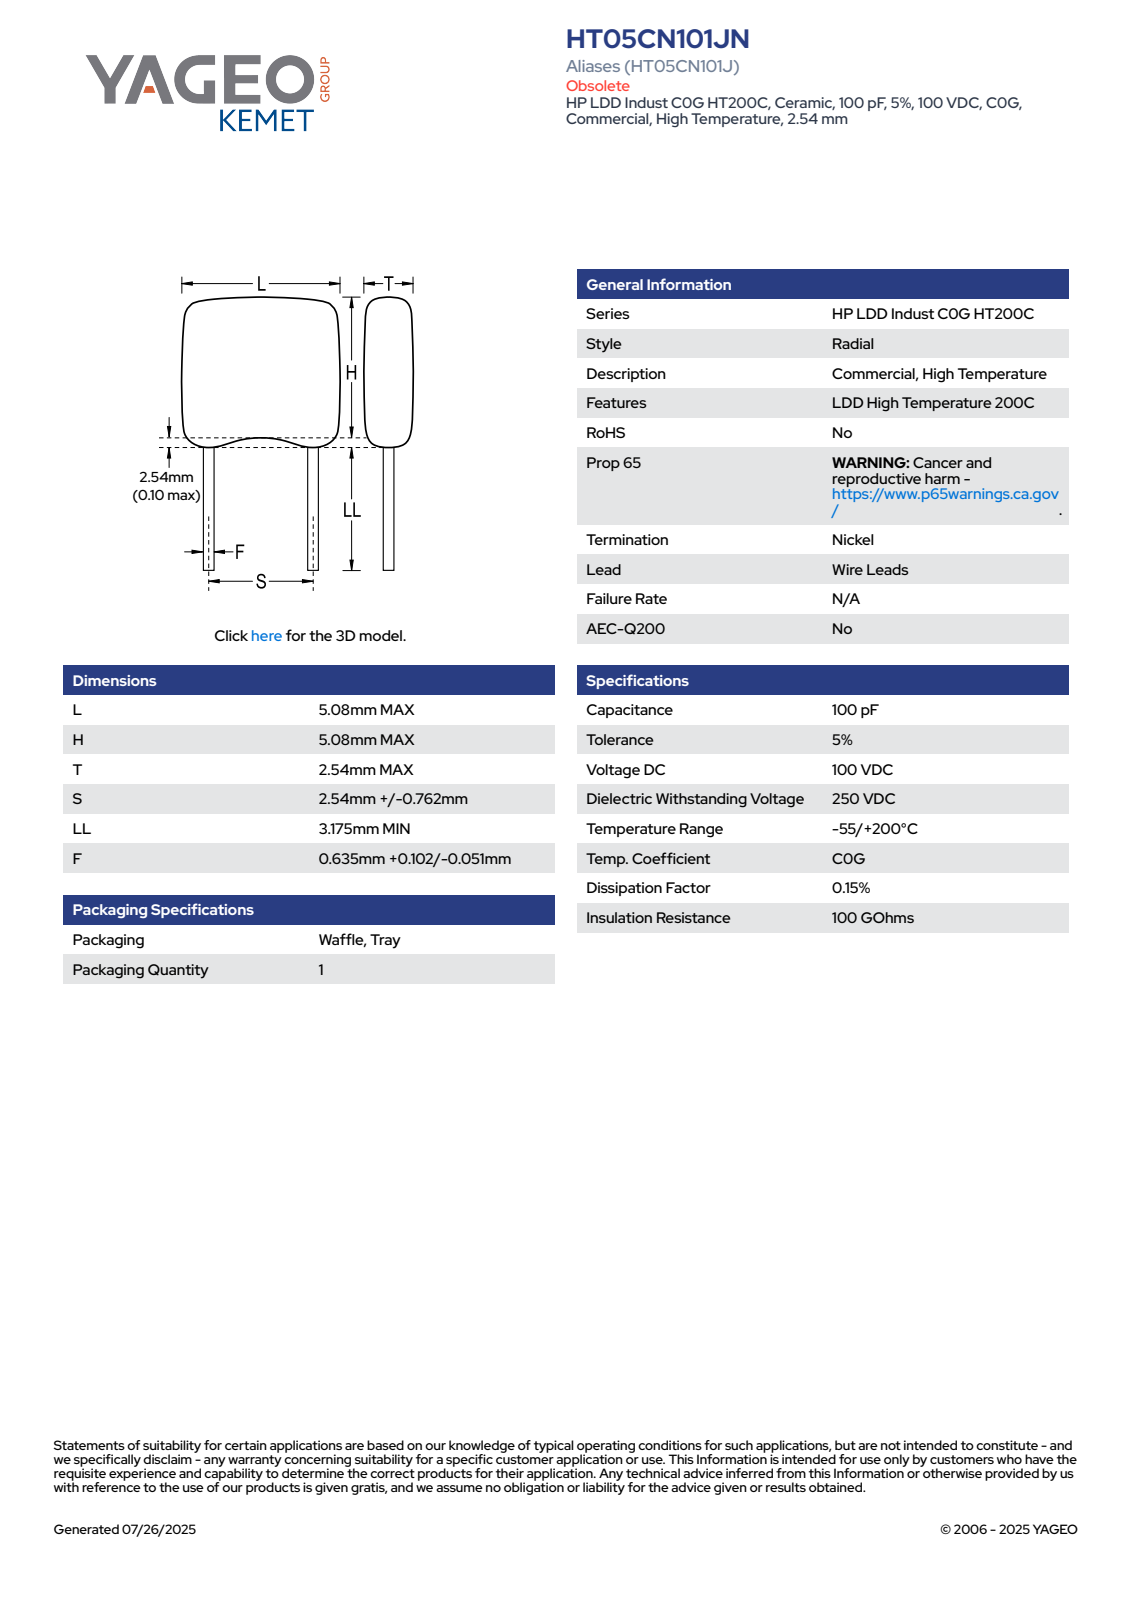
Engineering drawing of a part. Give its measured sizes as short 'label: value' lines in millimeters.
name: CCR_RMST_HT05_L5.08H5.08T2.54S3.3LL31.75F0.635
written by: SolidWorks 2014 (AUTOMOTIVE_DESIGN)
unit: mm
bodies: 4 solids, 69 faces (65 planar, 4 cylindrical, 0 other)
size: 36.83 × 5.08 × 2.54
volume: 86 mm³; area: 234 mm²
bosses: 2× ⌀0.64
face distances: 2.54, 5.08, 31.75, 36.83, 0.81, 34.72, 2.97, 2.11, 33.91, 2.16
